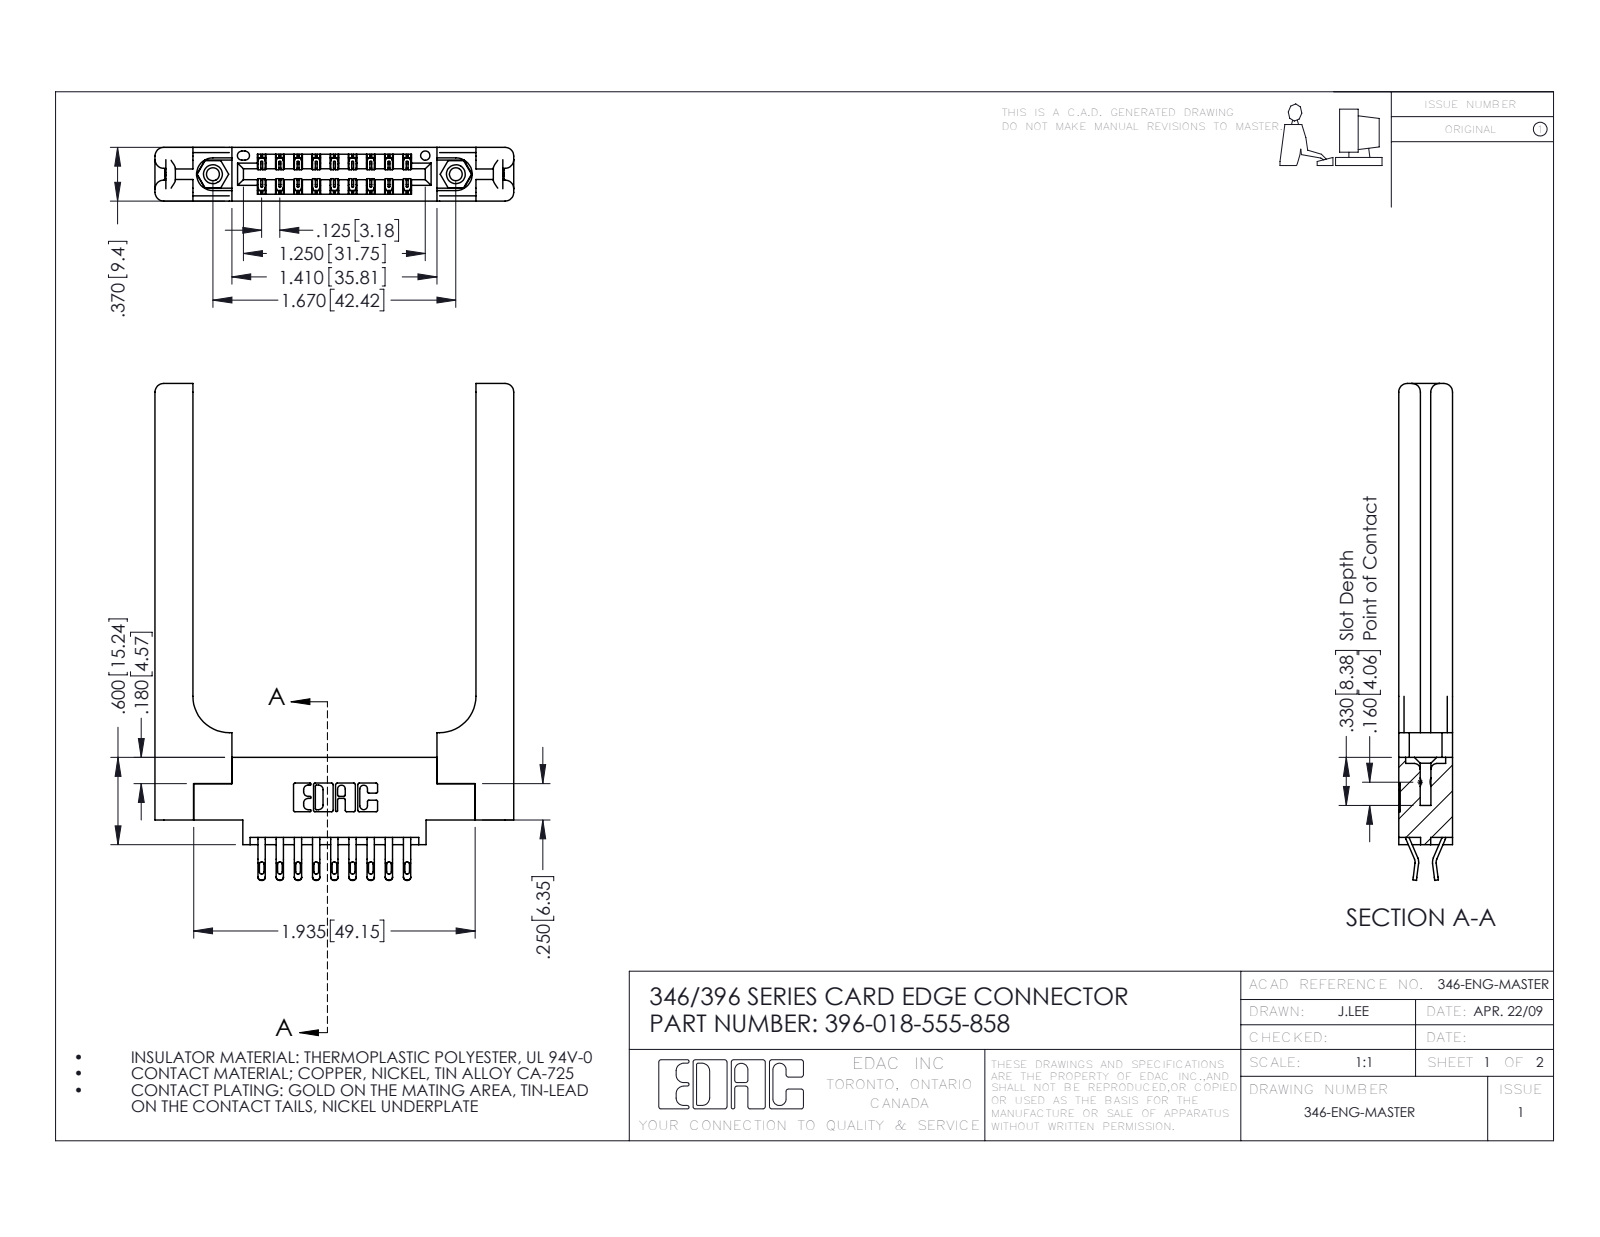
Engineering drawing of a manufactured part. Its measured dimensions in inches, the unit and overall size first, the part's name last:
Units: inches
Overall size (bounding box): 3.415 × 2.466 × 0.37
Round holes (diameter × count): ⌀0.089 ×2, ⌀0.125 ×2, ⌀0.156 ×2, ⌀0.064 ×1
Round bosses / shafts (diameter × count): ⌀0.155 ×2
Partial cylindrical surfaces — rounded edges, fillets, slot ends (radius × count): R0.016 ×36, R0.02 ×36, R0.006 ×27, R0.01 ×22, R0.06 ×16, R0.007 ×6, R0.031 ×6, R0.026 ×3
Main face-to-face distances: 0.37, 0.15, 0.22, 0.072, 0.148, 0.102, 0.048, 0.322, 0.173, 0.25
Hole centre spacings: 0.246, 1.465, 1.67
Volume: 0.808 in³ · Surface area: 19.72 in²
Bodies: 23 solids, 1426 faces (822 planar, 544 cylindrical, 60 other)
Part name (STEP PRODUCT): 346-220-058_345-220-058; 346 Part_0.170 Offset - 0.156 Dia-TH; 396-018-555-858; 345-292-001_555 Tail (+1 more)
STEP written by: SolidWorks 2016 (CONFIG_CONTROL_DESIGN)
